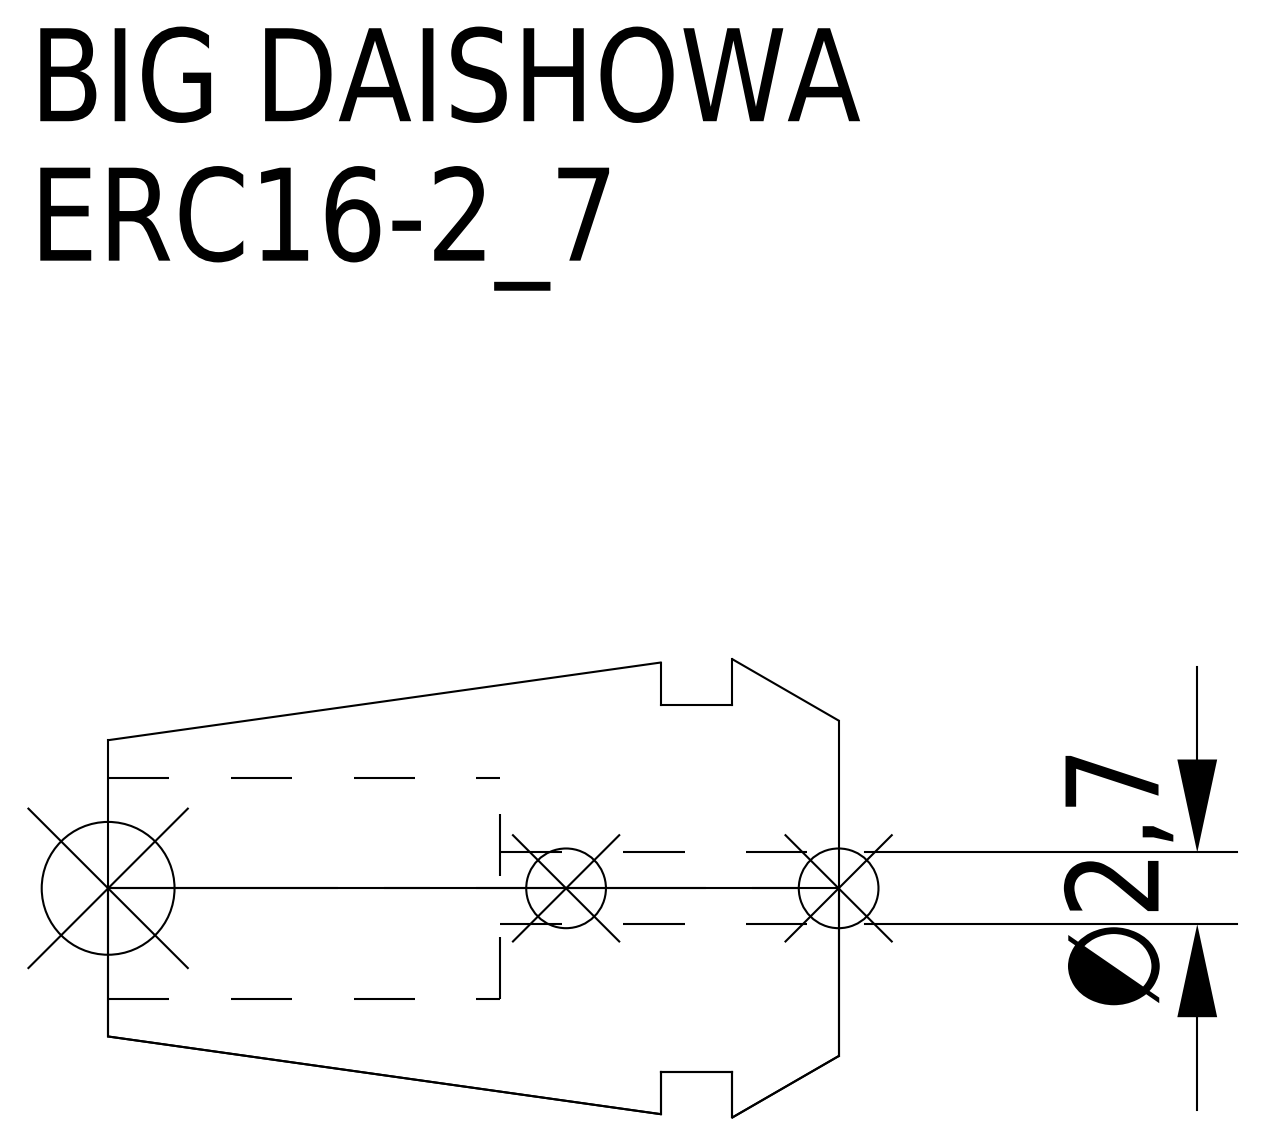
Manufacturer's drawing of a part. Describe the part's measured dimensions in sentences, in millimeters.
The part is named "ERC16-2_7". Its 3-D file was written by "CREO PARAMETRIC BY PTC INC, 2016380 (AUTOMOTIVE_DESIGN)". It is 1 solid with 15 faces: 5 planar, 6 cylindrical and 4 other. Overall it measures 27.5 by 17.25 by 17.25 millimeters. Its volume is 3 523 cubic millimeters and its surface area 2 129 square millimeters. Round holes: 1 of diameter 2.7, 1 of diameter 8.3. Round bosses or shafts: 1 of diameter 13.8. The main face-to-face distances are 4, 6.7, 2.7, 12.73, 8.73, 6.03, 27.5, 23.5, 20.8, 14.77.
